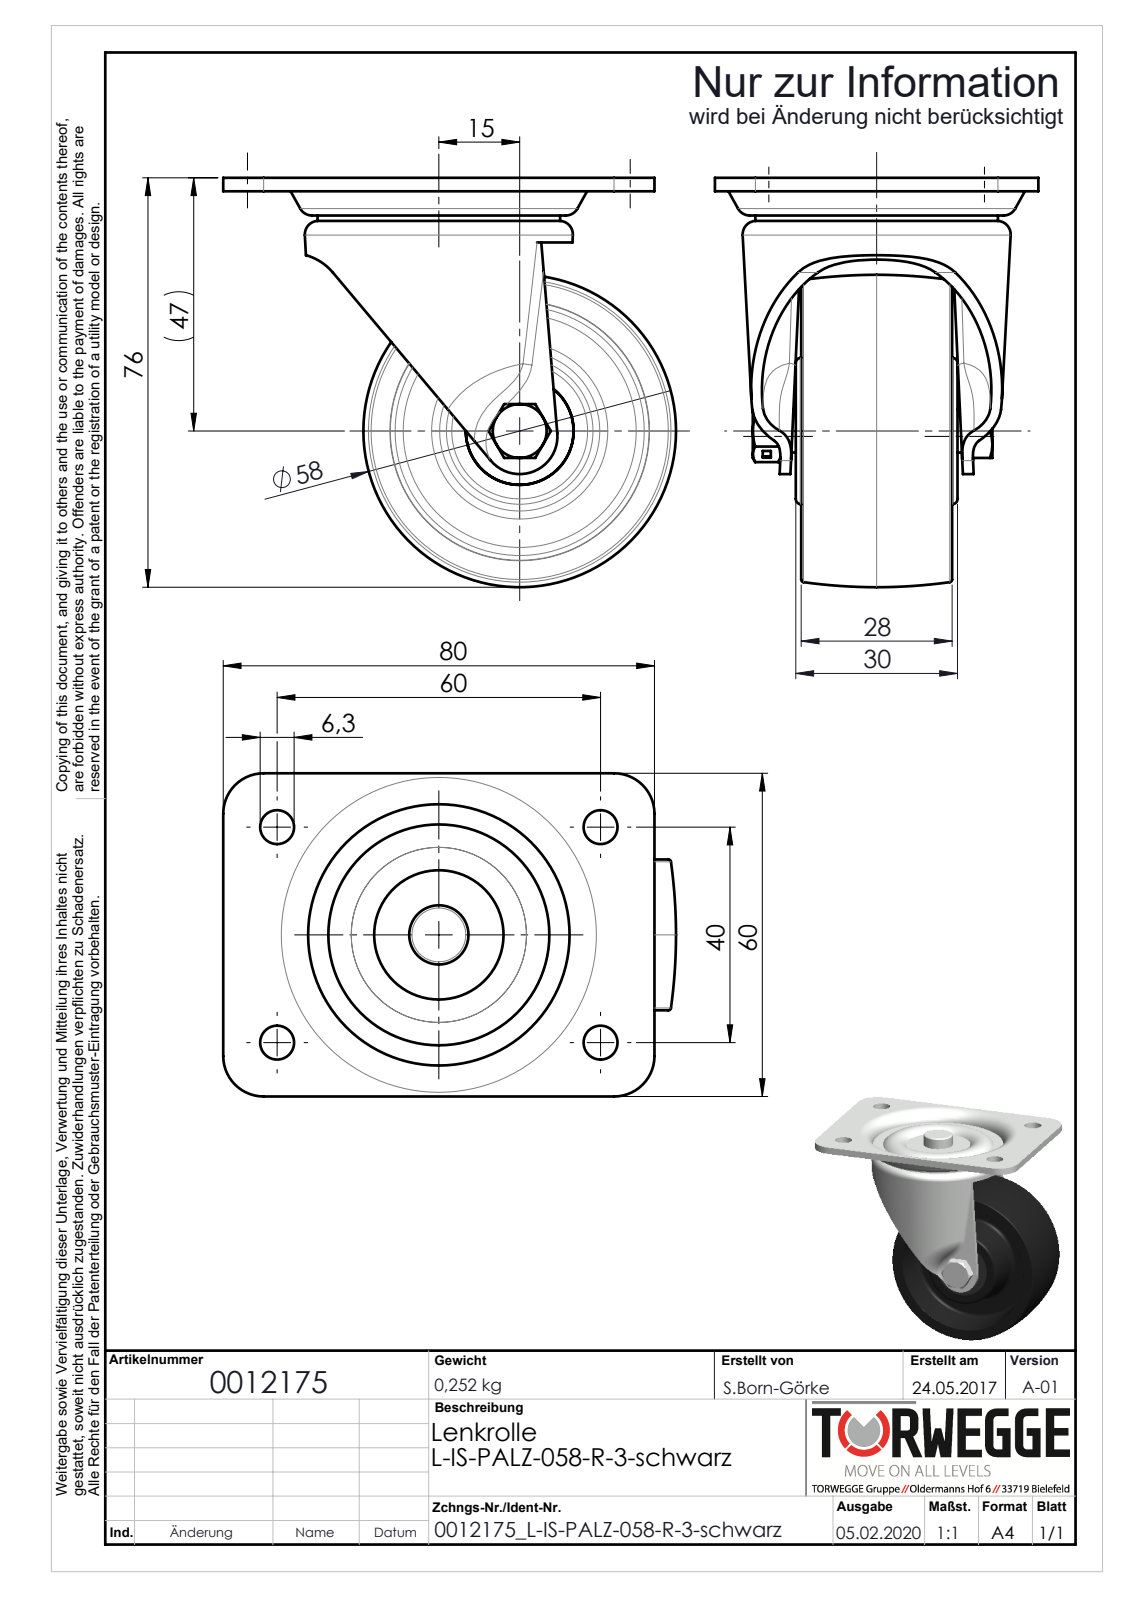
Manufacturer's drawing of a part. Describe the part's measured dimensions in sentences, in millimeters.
The part is named "0012175_L-IS-PALZ-058-R-3-schwarz_(A-01)". Its 3-D file was written by "SolidWorks 2018 (AUTOMOTIVE_DESIGN)". It is 6 solids with 211 faces: 71 planar, 41 cylindrical and 99 other. Overall it measures 84 by 76 by 60 millimeters. Its volume is 69 991 cubic millimeters and its surface area 40 913 square millimeters. Round holes: 4 of diameter 6.3, 1 of diameter 5, 1 of diameter 6, 1 of diameter 6.2, 1 of diameter 6.5, 1 of diameter 12, 1 of diameter 20. Round bosses or shafts: 1 of diameter 45, 1 of diameter 11, 1 of diameter 10, 1 of diameter 8. Partial cylindrical surfaces (rounded edges, fillets, slot ends): 4 of radius 7.5, 1 of radius 7, 1 of radius 10. The main face-to-face distances are 2.5, 10, 7.5, 2, 12.5, 15.5, 4.5, 5.5, 1, 3. The hole center spacings are 40, 60, 72.11.
